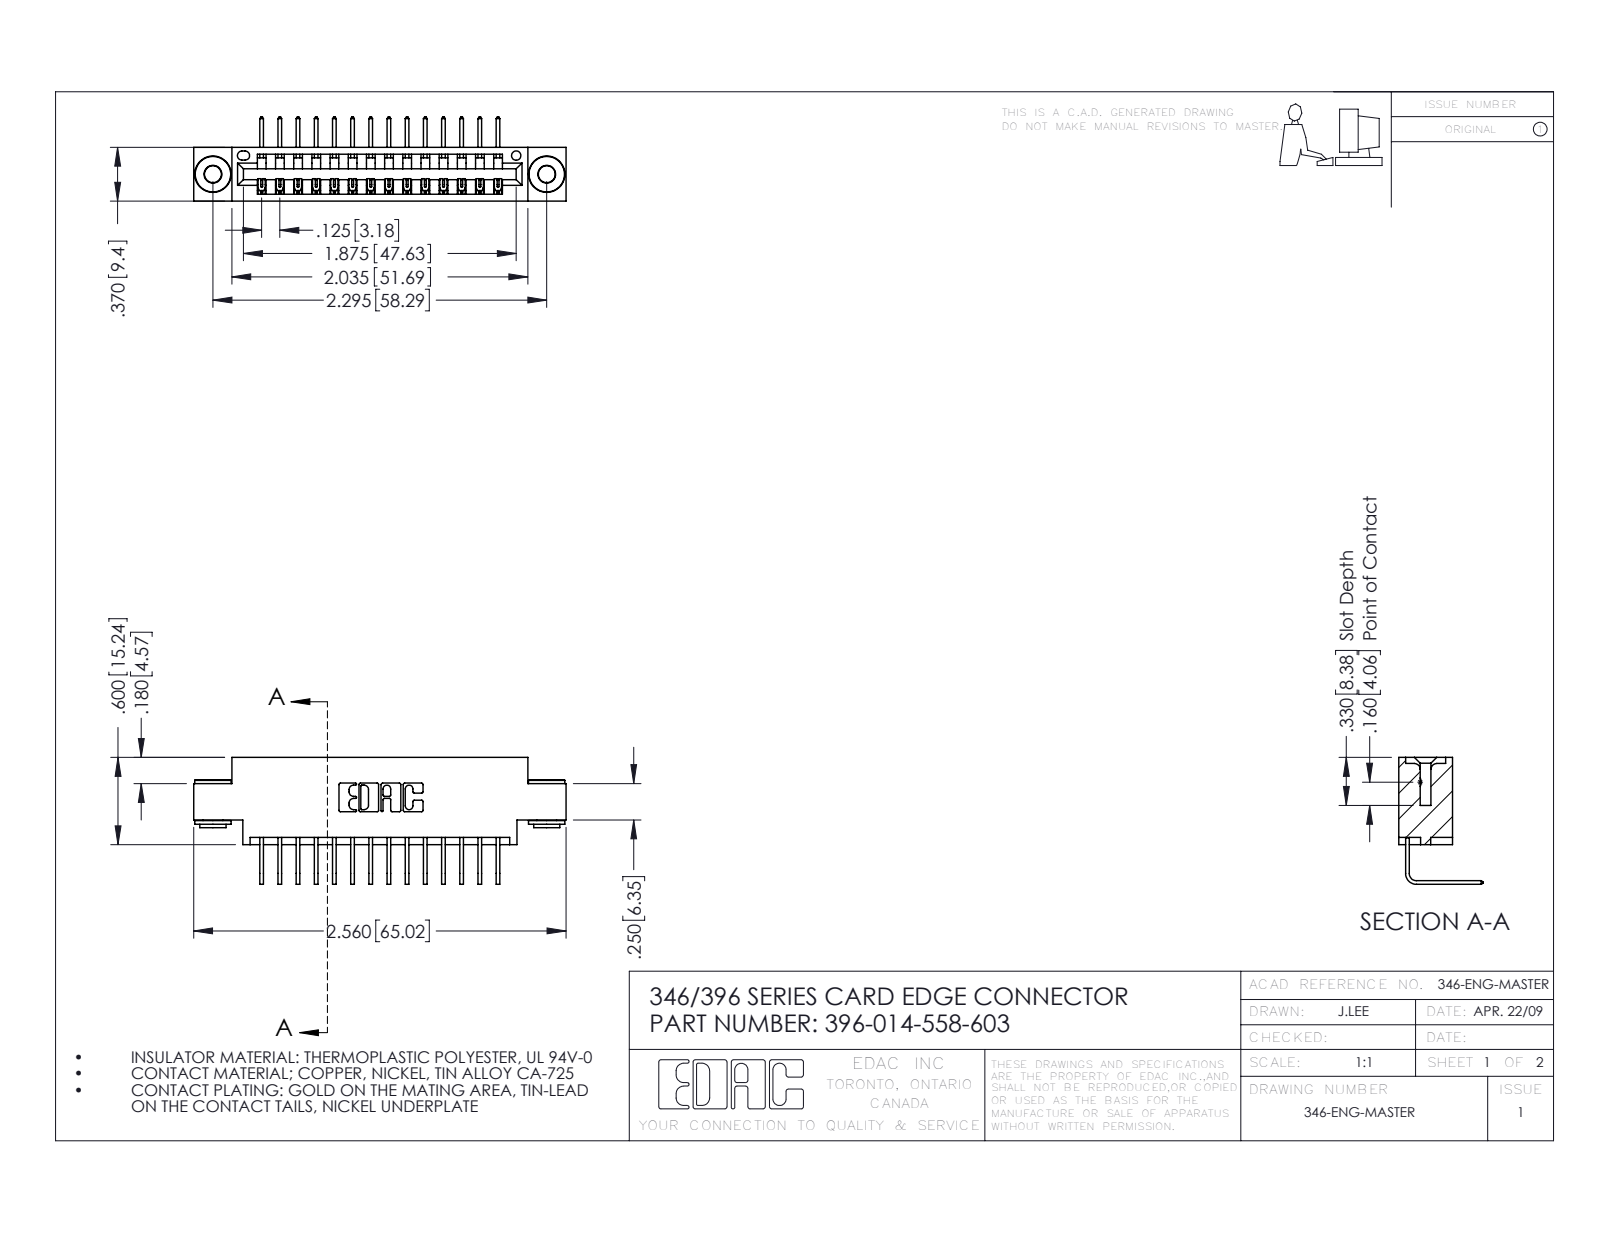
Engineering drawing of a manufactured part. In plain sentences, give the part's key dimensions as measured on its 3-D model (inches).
The part is named "345-250-002_345-250-002-102; 345-292-001_558 Tail - 2; 346 Part_0.170 Offset - 0.156 Dia-TH; 396-014-558-603". Its 3-D file was written by "SolidWorks 2016 (CONFIG_CONTROL_DESIGN)". It is 17 solids with 1004 faces: 678 planar, 318 cylindrical and 8 other. Overall it measures 2.56 by 0.873 by 0.58 inches. Its volume is 0.363 cubic inches and its surface area 12.06 square inches. Round holes: 2 of diameter 0.116, 2 of diameter 0.156, 1 of diameter 0.064. Round bosses or shafts: 2 of diameter 0.25, 2 of diameter 0.18, 2 of diameter 0.136. Partial cylindrical surfaces (rounded edges, fillets, slot ends): 28 of radius 0.006, 22 of radius 0.01, 6 of radius 0.007, 6 of radius 0.031, 3 of radius 0.026, 2 of radius 0.031, 2 of radius 0.04, 1 of radius 0.014. The main face-to-face distances are 0.322, 0.37, 0.048, 0.25, 0.025, 0.298, 0.072, 0.148, 0.222, 0.1. The hole center spacings are 0.246, 2.089, 2.295.
